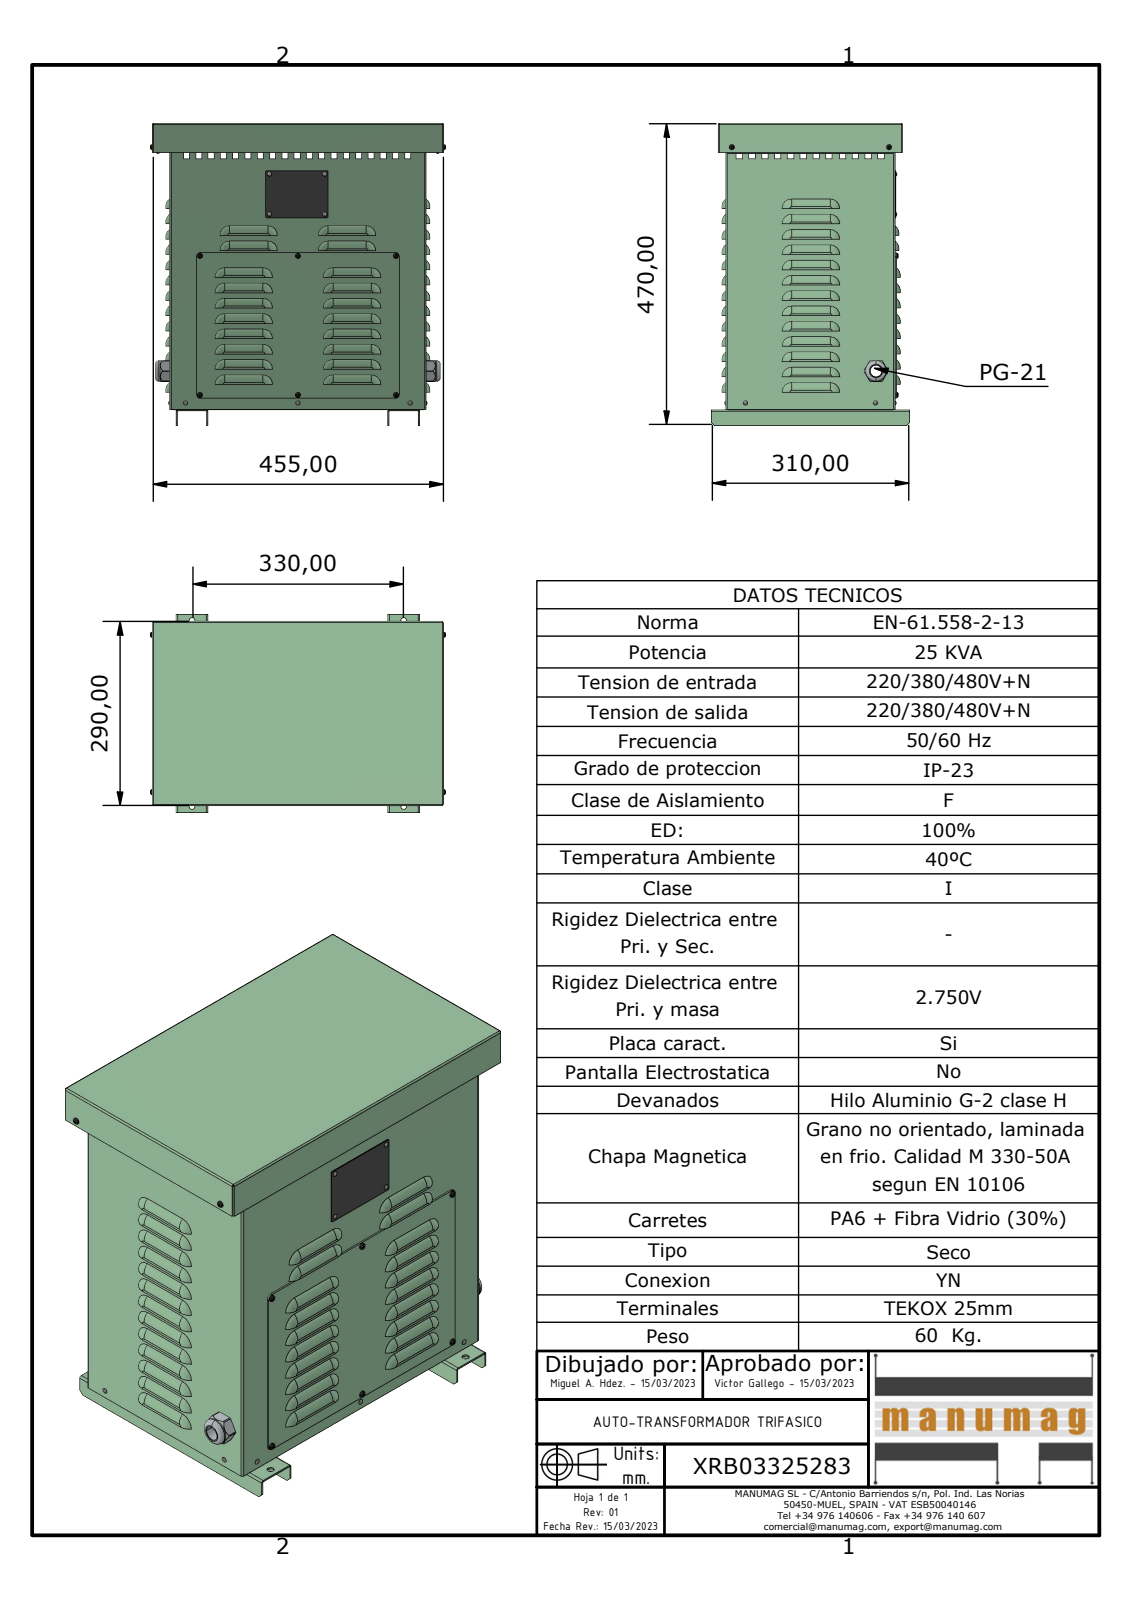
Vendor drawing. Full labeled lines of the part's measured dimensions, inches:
Part name (STEP PRODUCT): XRB03325283; JE015 - JE020 - JE025 EXPORT CUERPO; JE015 - JE020 - JE025 EXPORT BASE; JE015 - JE020 - JE025 EXPORT PATA (+6 more)
STEP written by: Autodesk Inventor 2023 (AUTOMOTIVE_DESIGN)
Units: inches
Bodies: 33 solids, 2242 faces (1225 planar, 489 cylindrical, 528 other)
Overall size (bounding box): 18.679 × 18.256 × 12.205
Volume: 142.9 in³ · Surface area: 3 252 in²
Round holes (diameter × count): ⌀0.134 ×17, ⌀0.157 ×9, ⌀0.091 ×8, ⌀0.354 ×6, ⌀0.201 ×3, ⌀0.351 ×2, ⌀0.709 ×1, ⌀1.177 ×1
Round bosses / shafts (diameter × count): ⌀0.126 ×9, ⌀0.157 ×8, ⌀0.143 ×8, ⌀1.276 ×1, ⌀1.122 ×1, ⌀1.114 ×1
Partial cylindrical surfaces — rounded edges, fillets, slot ends (radius × count): R0.551 ×118, R0.157 ×63, R0.591 ×49, R0.079 ×10, R0.079 ×9, R0.137 ×8, R0.02 ×6, R0.098 ×6
Main face-to-face distances: 0.079, 10.351, 10.43, 15.78, 17.609, 17.688, 10.272, 15.701, 15.858, 0.157
Hole centre spacings: 8.587, 6.055, 6.067, 10.507, 10.514, 12.122, 13.082, 14.855
